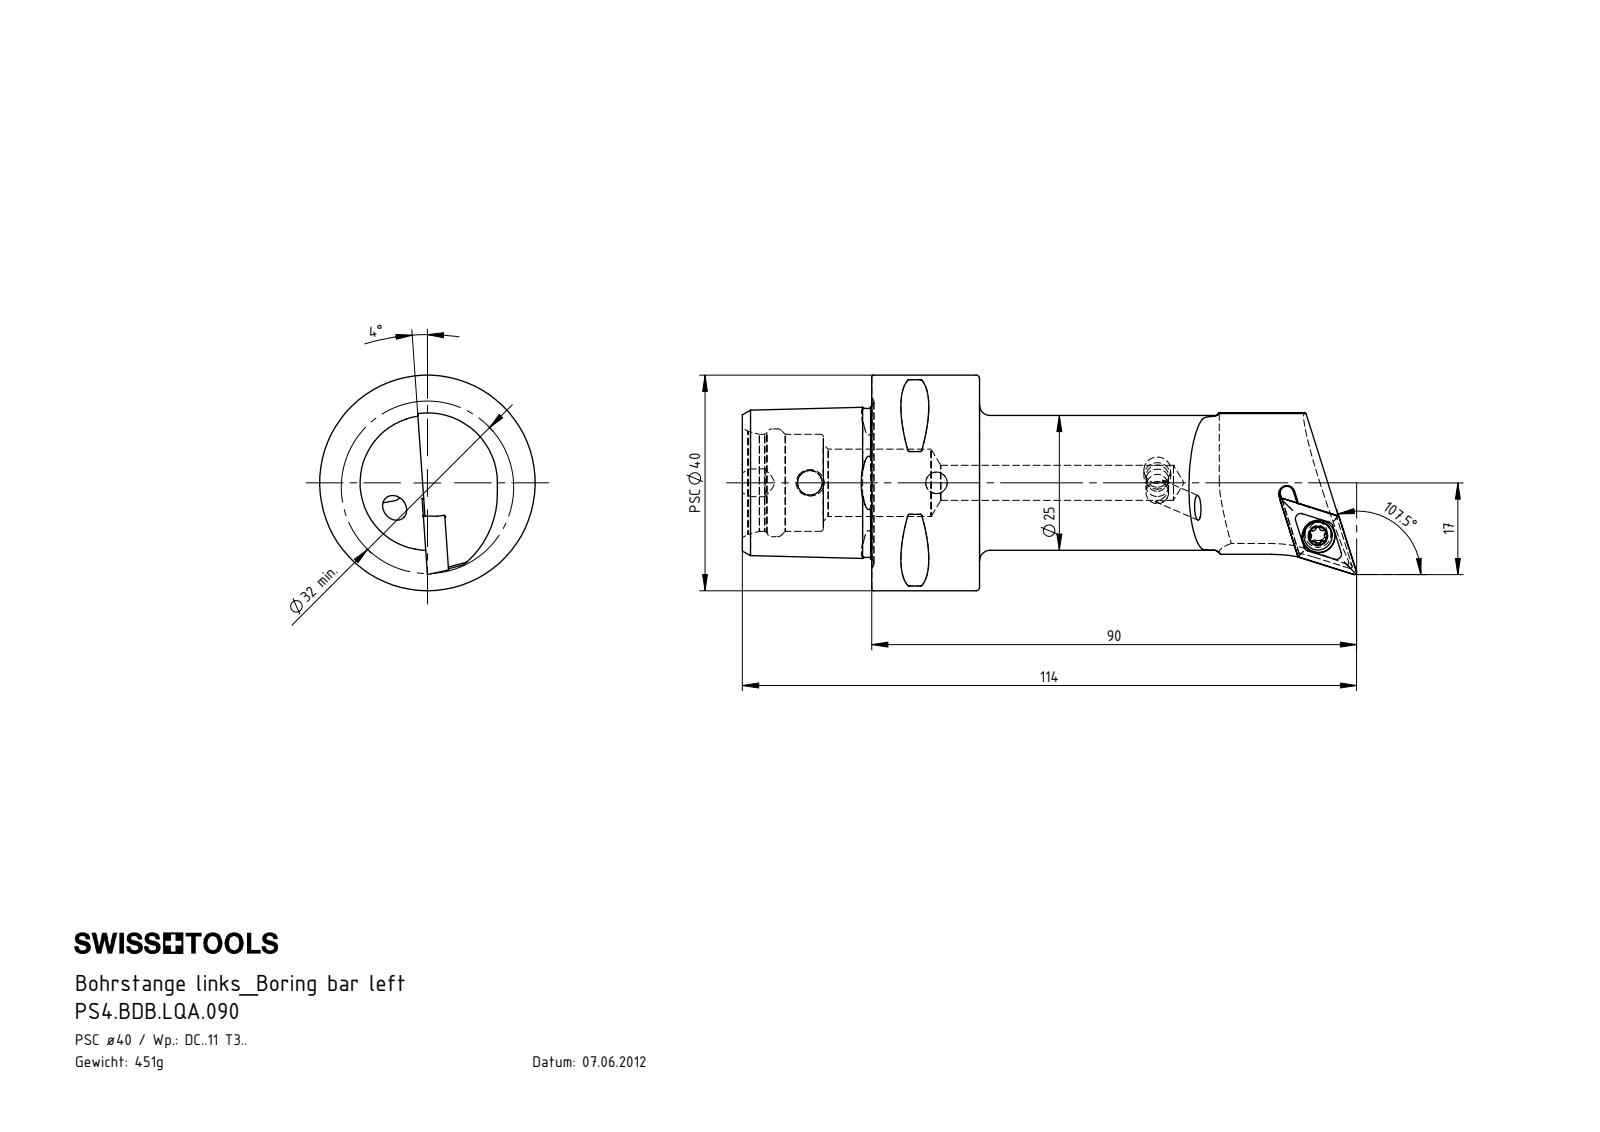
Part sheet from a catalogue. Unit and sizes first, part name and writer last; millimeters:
Units: millimetres
Overall size (bounding box): 114 × 40 × 40
Round holes (diameter × count): ⌀4 ×2, ⌀4.2 ×2, ⌀3.3 ×1, ⌀4.4 ×1, ⌀4.6 ×1, ⌀5 ×1, ⌀6.1 ×1, ⌀6.5 ×1, ⌀12.5 ×1, ⌀18 ×1, ⌀20 ×1
Round bosses / shafts (diameter × count): ⌀40 ×1, ⌀25 ×1, ⌀5.25 ×1, ⌀5 ×1, ⌀4 ×1
Partial cylindrical surfaces — rounded edges, fillets, slot ends (radius × count): R0.3 ×8, R0.34 ×6, R0.59 ×6, R3 ×2, R1.25 ×1, R13 ×1, R17 ×1, R26 ×1
Main face-to-face distances: 20, 24, 44, 3.67, 15.52, 35.3, 15, 9, 29, 23.8
Hole centre spacings: 23.5
Volume: 57 209 mm³ · Surface area: 15 667 mm²
Bodies: 5 solids, 296 faces (53 planar, 75 cylindrical, 168 other)
Part name (STEP PRODUCT): KVT_MB_600_050; DCMT11T304; WCB-ER2.001.009_A; PS4-BDB.LQA.090 (+1 more)
STEP written by: SolidWorks 2012 (CONFIG_CONTROL_DESIGN)
